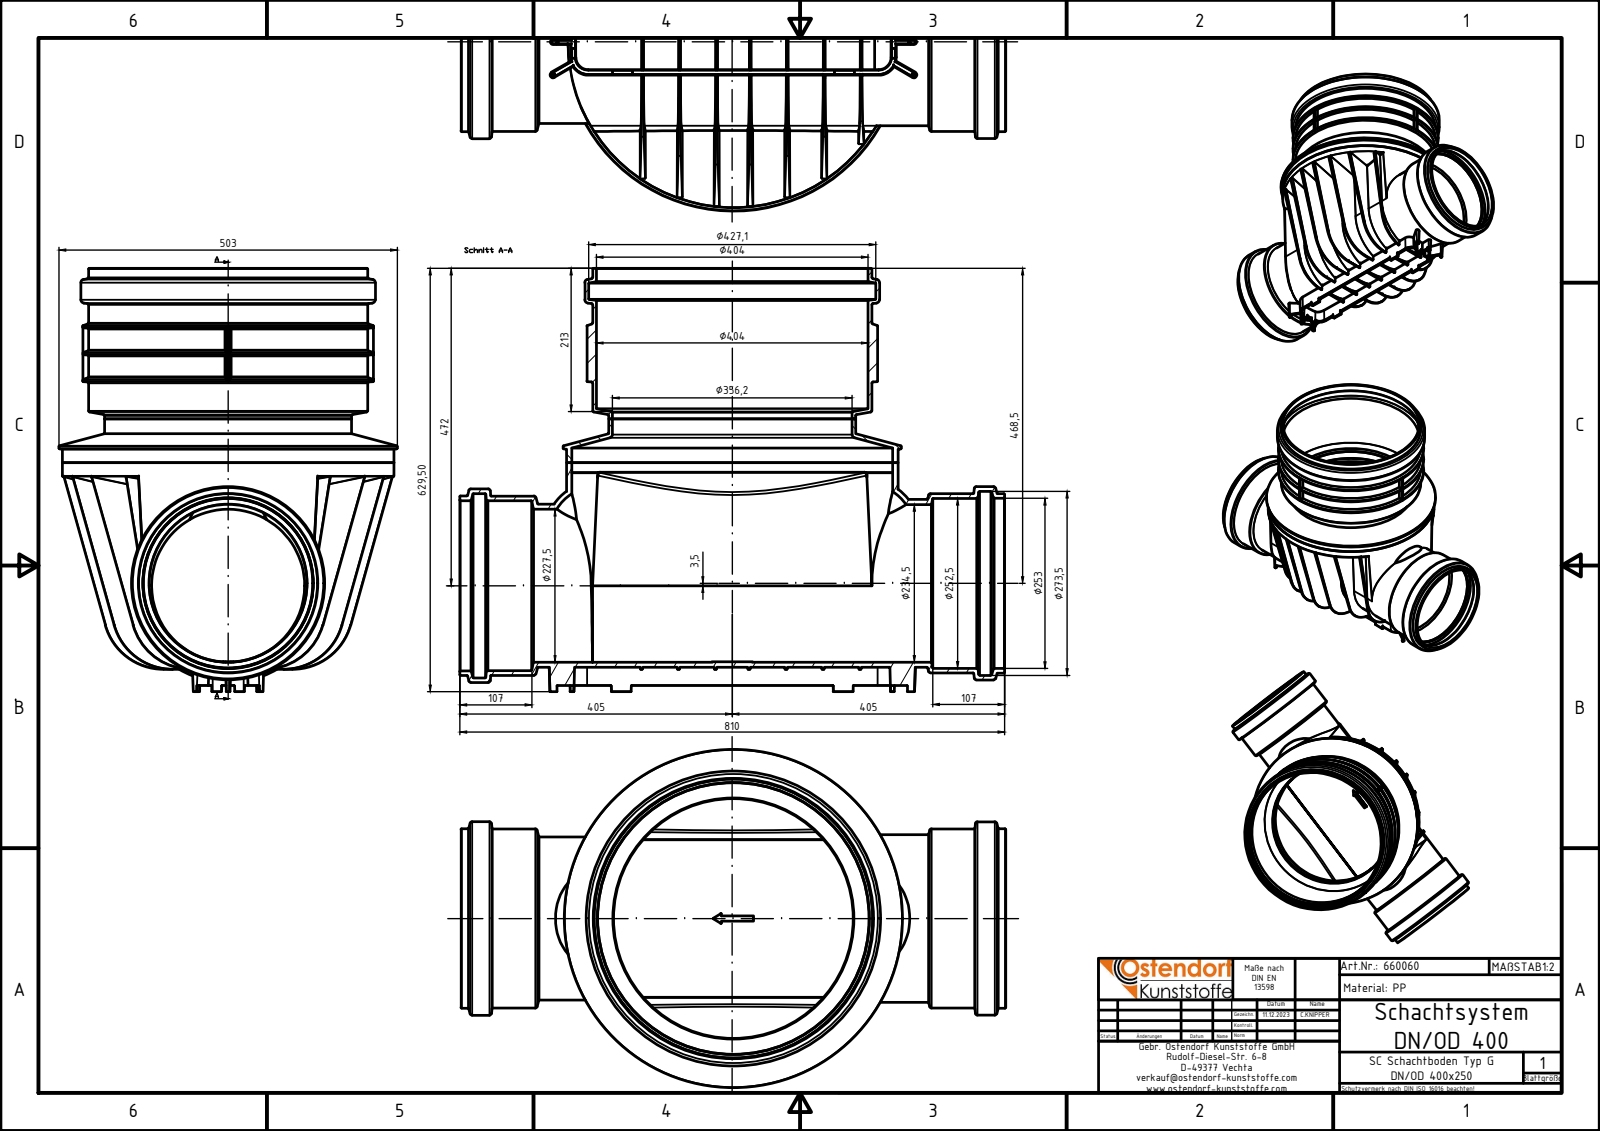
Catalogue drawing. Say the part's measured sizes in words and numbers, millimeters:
The part is named "660060z; 660060 Teil 1; 660060 Teil 2; 660060 Teil 3". Its 3-D file was written by "Autodesk Inventor 2024 (AUTOMOTIVE_DESIGN)". It is 3 solids with 1126 faces: 206 planar, 340 cylindrical and 580 other. Overall it measures 810 by 629.5 by 503 millimeters. Its volume is 10 010 000 cubic millimeters and its surface area 3 116 000 square millimeters. Round holes: 2 of diameter 252.5, 2 of diameter 253, 1 of diameter 227.5, 1 of diameter 234.5, 1 of diameter 273.5, 1 of diameter 274, 1 of diameter 356.2, 1 of diameter 404, 1 of diameter 427.1, 1 of diameter 477. Round bosses or shafts: 2 of diameter 267, 2 of diameter 266.5, 1 of diameter 503, 1 of diameter 493, 1 of diameter 438.1, 1 of diameter 432, 1 of diameter 415, 1 of diameter 367.2. Partial cylindrical surfaces (rounded edges, fillets, slot ends): 173 of radius 0.5, 8 of radius 90, 6 of radius 2.75, 1 of radius 113.8. The main face-to-face distances are 55, 160, 105, 110, 215, 50, 270, 90.5, 65, 324.91. The hole center spacings are 3.5.
